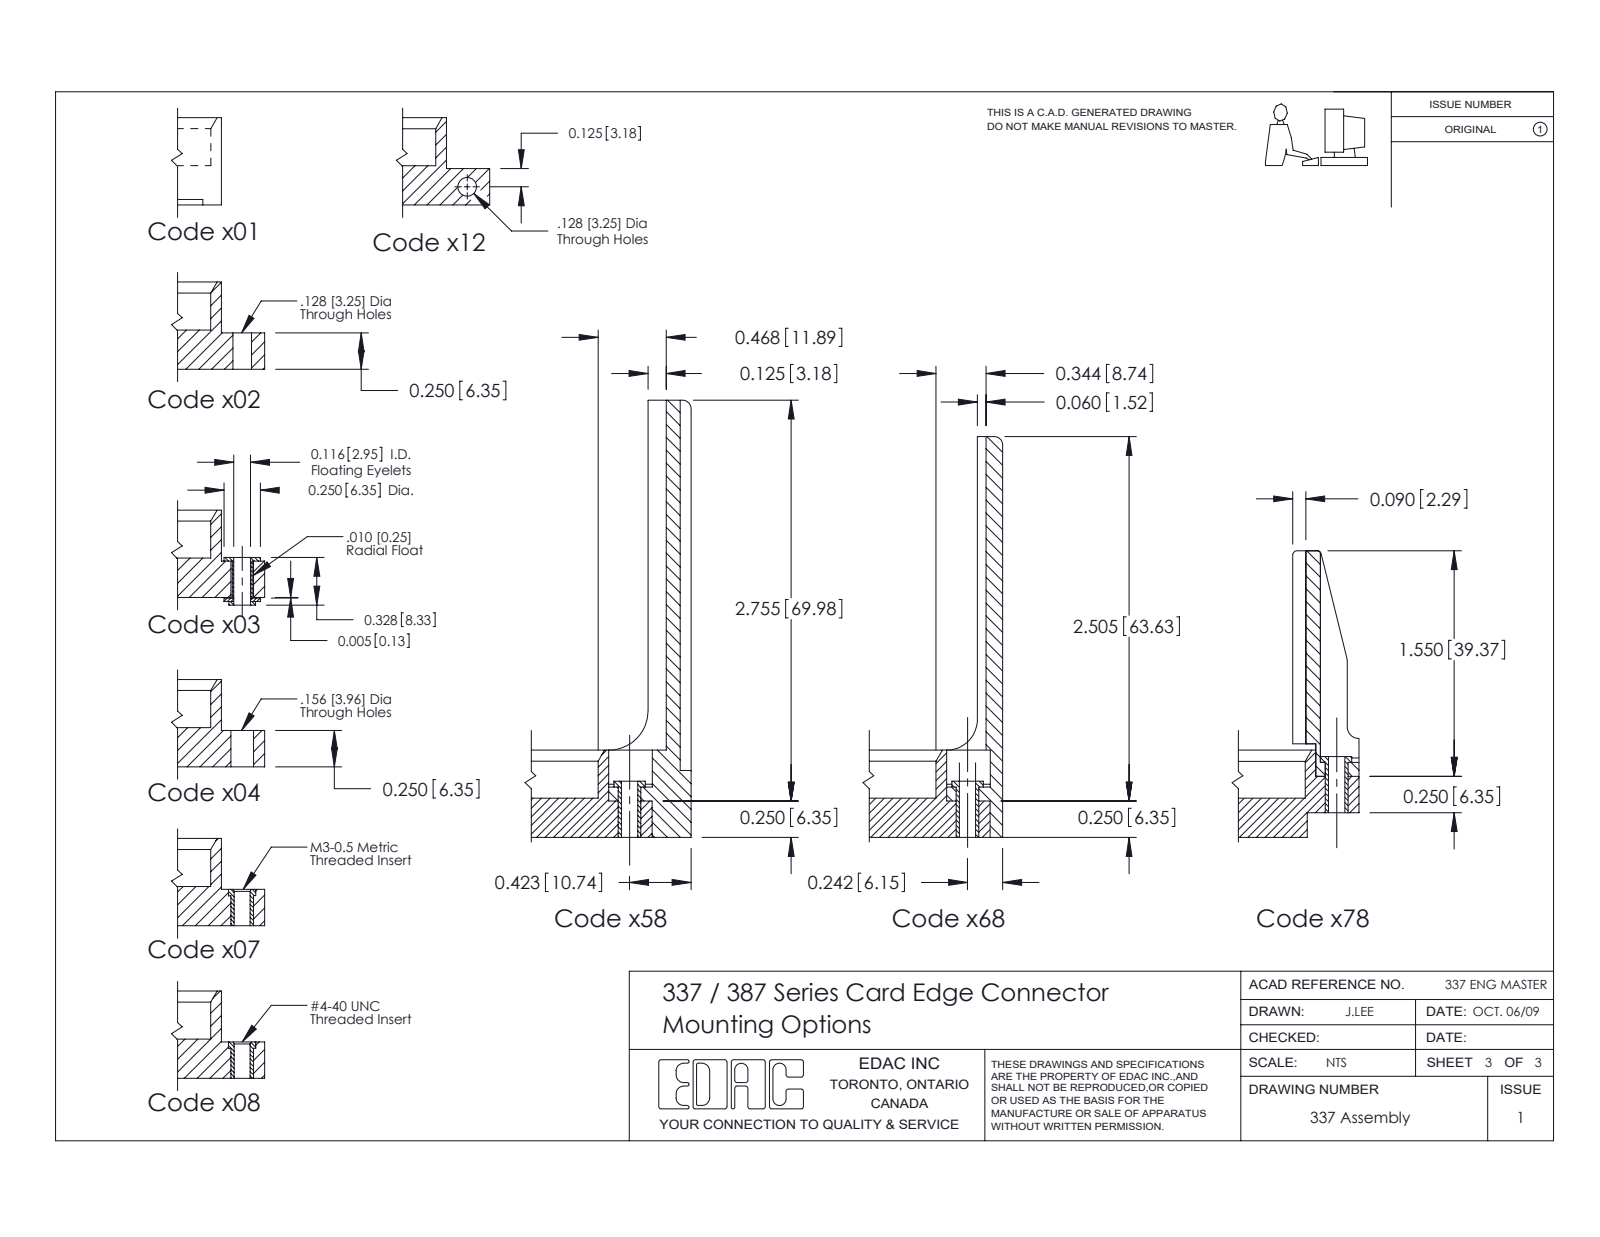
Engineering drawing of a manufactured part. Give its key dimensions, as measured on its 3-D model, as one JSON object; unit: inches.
{"part_name": "337 Part_Flush Mounting Lugs - 0.128 Dia; 387-009-544-102; 345-292-001_345-293-144", "step_written_by": "SolidWorks 2016 (CONFIG_CONTROL_DESIGN)", "units": "inches", "bodies": {"solids": 10, "faces": 618, "planar": 448, "cylindrical": 170, "other": 0}, "overall_size": [2.31, 1.35, 0.37], "volume_in3": 0.351, "surface_area_in2": 9.044, "round_holes": [[0.128, 2]], "partial_cylinders_radius": [[0.01, 22], [0.006, 18], [0.007, 6], [0.031, 6], [0.026, 3], [0.014, 1], [0.022, 1], [0.024, 1]], "face_to_face_distances": [0.072, 0.298, 0.37, 0.098, 0.272, 0.025, 0.2, 0.149, 0.156, 0.05], "hole_center_spacings": [2]}
